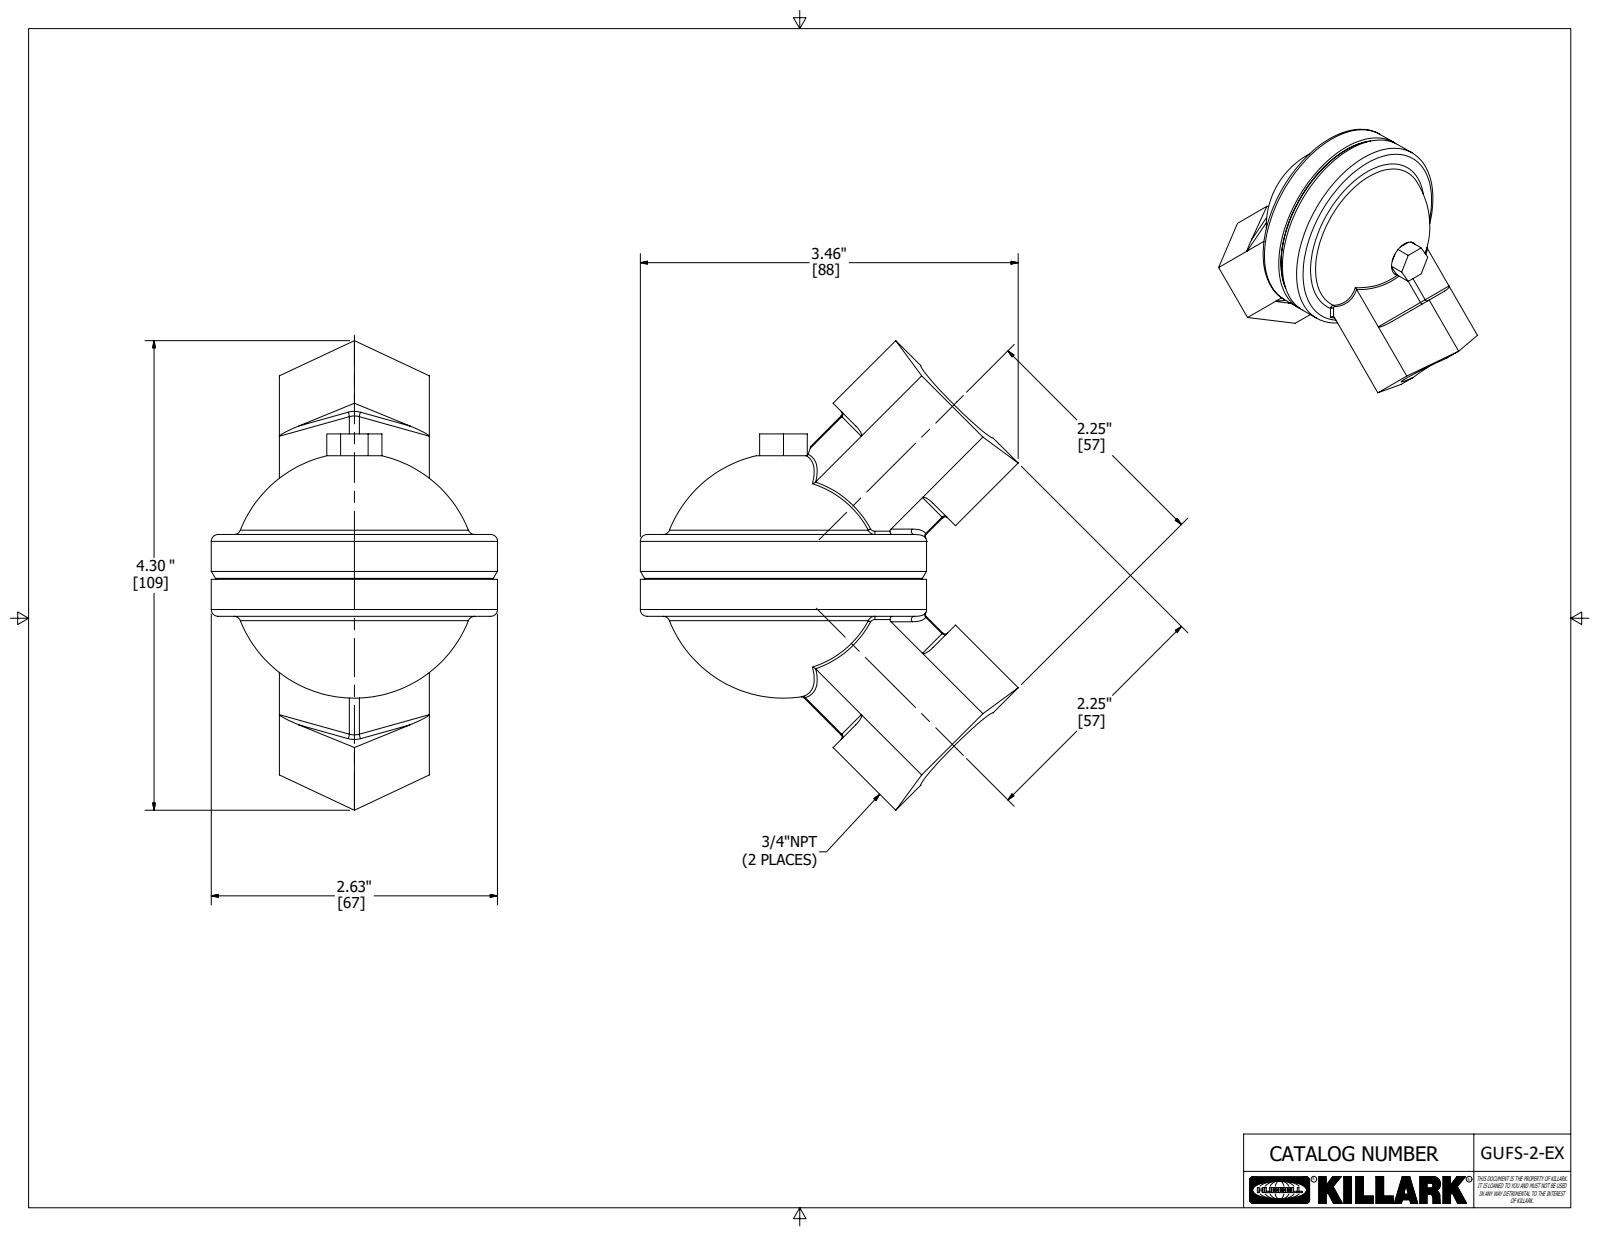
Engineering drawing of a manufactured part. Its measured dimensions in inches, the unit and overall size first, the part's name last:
Units: inches
Overall size (bounding box): 4.305 × 3.465 × 2.625
Round holes (diameter × count): ⌀0.792 ×2, ⌀0.875 ×2, ⌀0.252 ×1, ⌀0.375 ×1, ⌀0.5 ×1, ⌀1.625 ×1
Round bosses / shafts (diameter × count): ⌀2.625 ×1, ⌀0.625 ×1, ⌀0.373 ×1, ⌀0.313 ×1, ⌀0.31 ×1, ⌀0.242 ×1
Partial cylindrical surfaces — rounded edges, fillets, slot ends (radius × count): R0.031 ×16, R0.125 ×4
Main face-to-face distances: 1.374, 1.375, 0.348, 0.402, 0.75, 1.279, 0.055, 0.411, 0.063, 0.339
Volume: 6.677 in³ · Surface area: 65.79 in²
Bodies: 3 solids, 194 faces (72 planar, 37 cylindrical, 85 other)
Part name (STEP PRODUCT): GUFS-2; 0078418M; 0078419M; 06857AAEB
STEP written by: Autodesk Inventor 2020 (AUTOMOTIVE_DESIGN)
